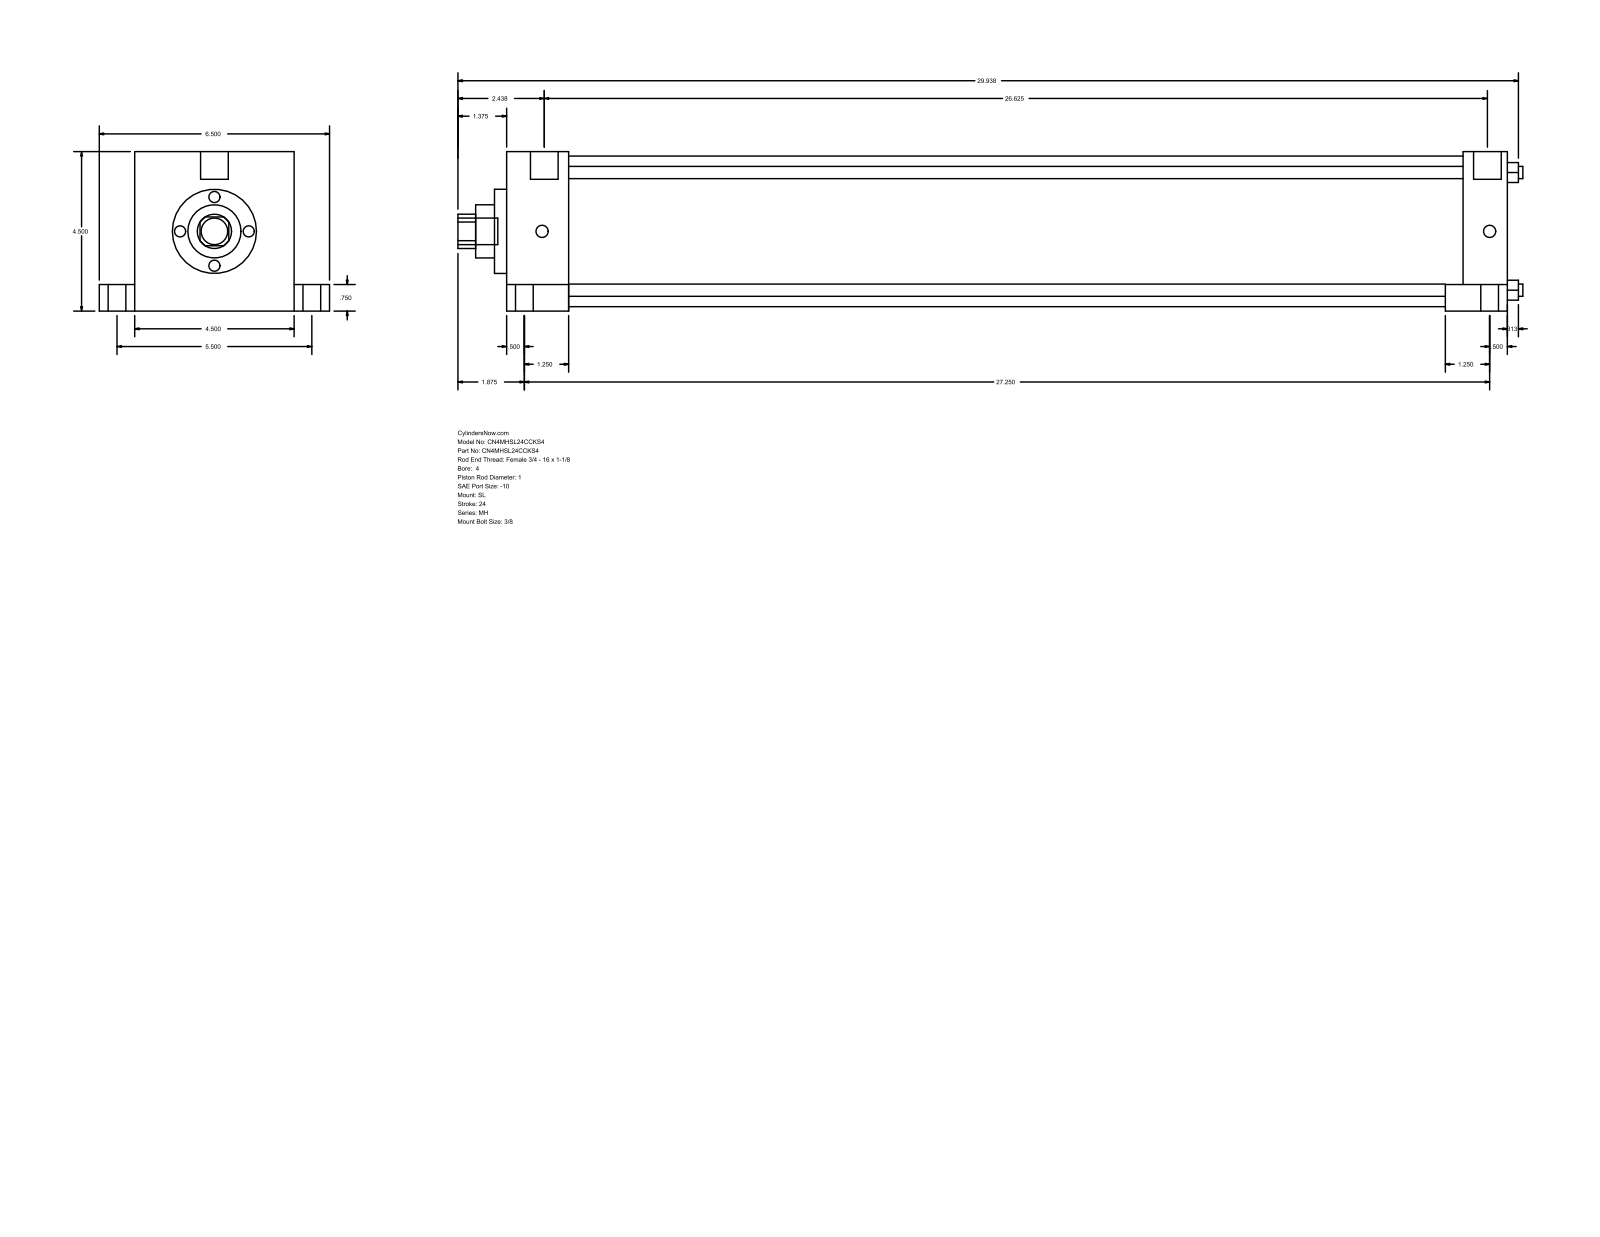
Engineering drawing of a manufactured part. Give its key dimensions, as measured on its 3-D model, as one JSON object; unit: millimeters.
{"part_name": "MH_SL__0400_1", "step_written_by": "GSSL Pune (CONFIG_CONTROL_DESIGN)", "units": "millimeters", "bodies": {"solids": 0, "faces": 110, "planar": 77, "cylindrical": 33, "other": 0}, "overall_size": [763.59, 165.1, 114.3], "round_holes": [[8.76, 4], [25.4, 1], [38.1, 1], [60.33, 1], [107.95, 1]], "round_bosses_or_shafts": [[19.05, 5], [12.7, 4], [8.73, 4], [19.84, 2]], "partial_cylinders_radius": [[12.29, 1]], "face_to_face_distances": [114.3, 717.56, 44.46, 673.1, 685.81, 641.35, 31.75, 25.4, 139.7, 19.05], "hole_center_spacings": [59.62, 84.32, 119.25]}
